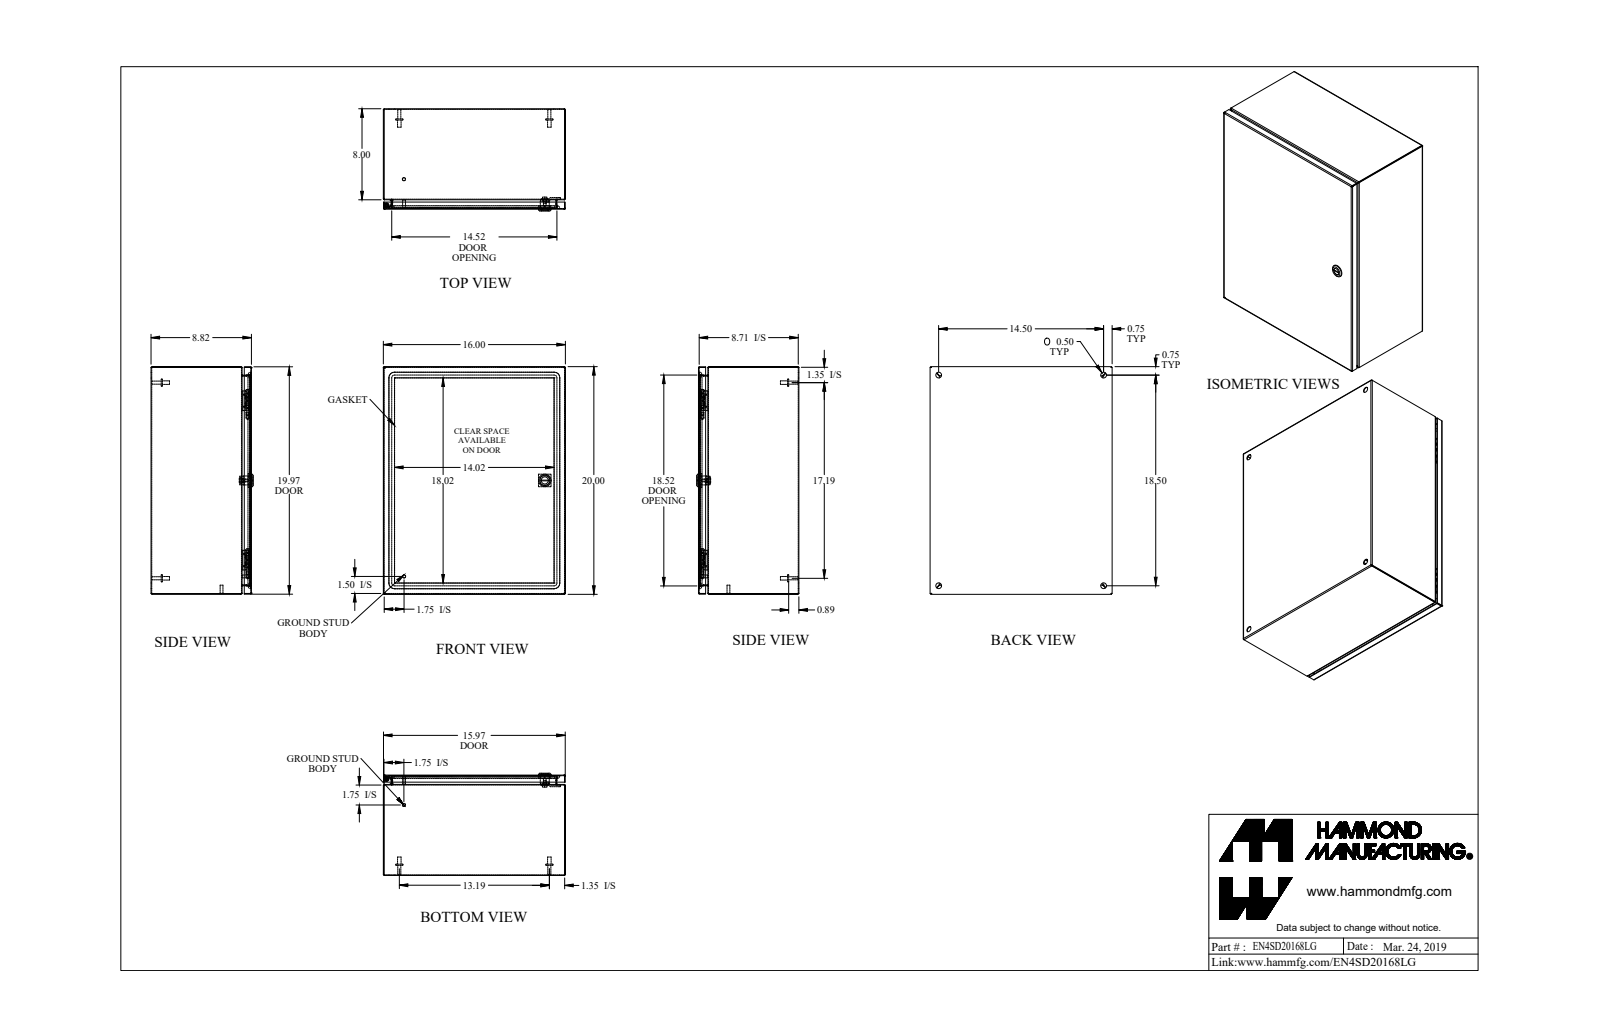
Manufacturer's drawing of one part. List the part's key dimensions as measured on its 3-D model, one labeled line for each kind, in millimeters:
Part name (STEP PRODUCT): EN4SD20168LG_Default
STEP written by: SolidWorks 2019 (CONFIG_CONTROL_DESIGN)
Units: millimetres
Bodies: 21 solids, 634 faces (285 planar, 213 cylindrical, 136 other)
Overall size (bounding box): 508 × 406.4 × 228.1
Volume: 1 384 000 mm³ · Surface area: 1 853 000 mm²
Round holes (diameter × count): ⌀12.7 ×4, ⌀4.4 ×1, ⌀5.9 ×1, ⌀6.1 ×1, ⌀6.1 ×1, ⌀15.9 ×1, ⌀19.9 ×1
Round bosses / shafts (diameter × count): ⌀15.9 ×4, ⌀8 ×4, ⌀6.9 ×4, ⌀7.1 ×2, ⌀6.4 ×2, ⌀27.9 ×1, ⌀13.3 ×1, ⌀11.6 ×1
Partial cylindrical surfaces — rounded edges, fillets, slot ends (radius × count): R0.7 ×21, R2.2 ×21, R6.4 ×16, R482.6 ×8, R0.2 ×4, R1.6 ×4, R12.7 ×4, R3.2 ×2
Main face-to-face distances: 1.4, 222.6, 221.2, 224.1, 405, 506.6, 403.5, 406.4, 505.1, 508
Hole centre spacings: 368.3, 469.9, 597.1, 236.5, 236.5, 414.4, 414.5
